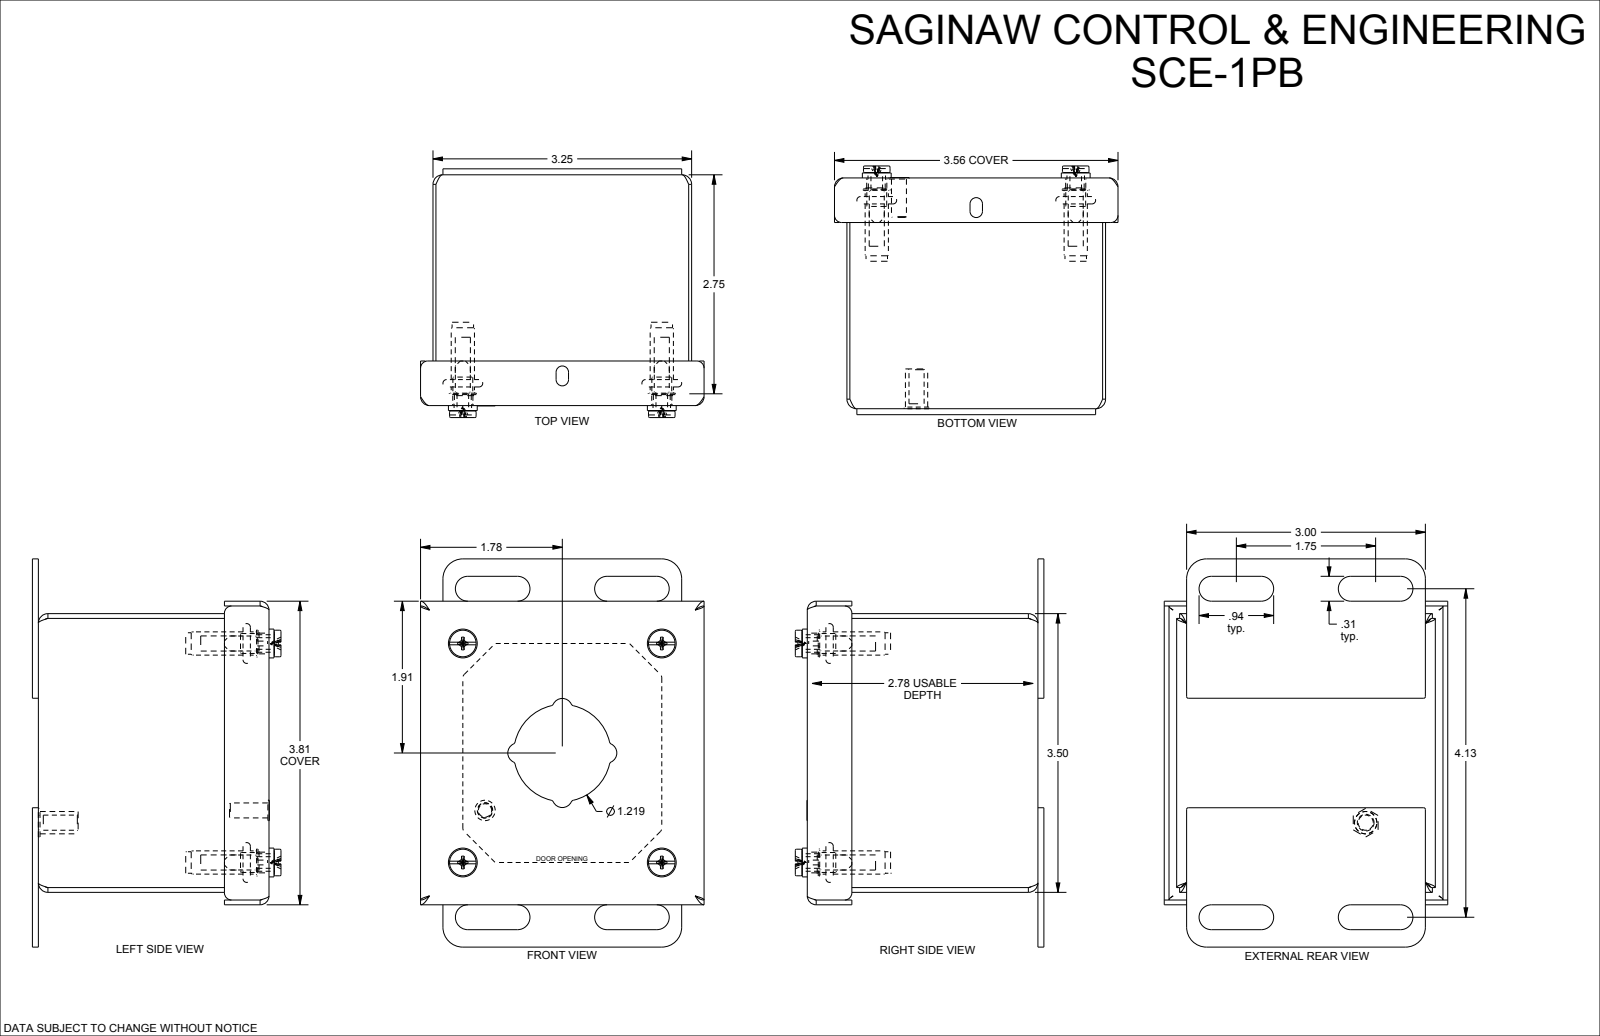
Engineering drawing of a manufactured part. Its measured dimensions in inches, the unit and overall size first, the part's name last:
Units: inches
Overall size (bounding box): 4.875 × 3.563 × 3.036
Round holes (diameter × count): ⌀0.19 ×5, ⌀0.22 ×4, ⌀0.25 ×4, ⌀0.25 ×4, ⌀0.317 ×4, ⌀0.193 ×1
Round bosses / shafts (diameter × count): ⌀0.362 ×4, ⌀0.34 ×4, ⌀0.292 ×4, ⌀0.27 ×4, ⌀0.26 ×4, ⌀0.28 ×1, ⌀0.256 ×1, ⌀0.188 ×1
Partial cylindrical surfaces — rounded edges, fillets, slot ends (radius × count): R0.06 ×16, R0.12 ×16, R0.015 ×8, R0.04 ×8, R0.115 ×8, R0.156 ×8, R0.245 ×8, R0.02 ×4
Main face-to-face distances: 0.06, 2.838, 3.19, 3.44, 2.898, 2.778, 0.075, 0.135, 2.913, 2.973
Hole centre spacings: 2.5, 3.717, 2.75, 2.5, 2.5, 3.716, 3.717, 0.707
Volume: 5.282 in³ · Surface area: 176 in²
Bodies: 15 solids, 403 faces (158 planar, 177 cylindrical, 68 other)
Part name (STEP PRODUCT): SCE-1PB
STEP written by: SolidWorks 2019 (AUTOMOTIVE_DESIGN)
